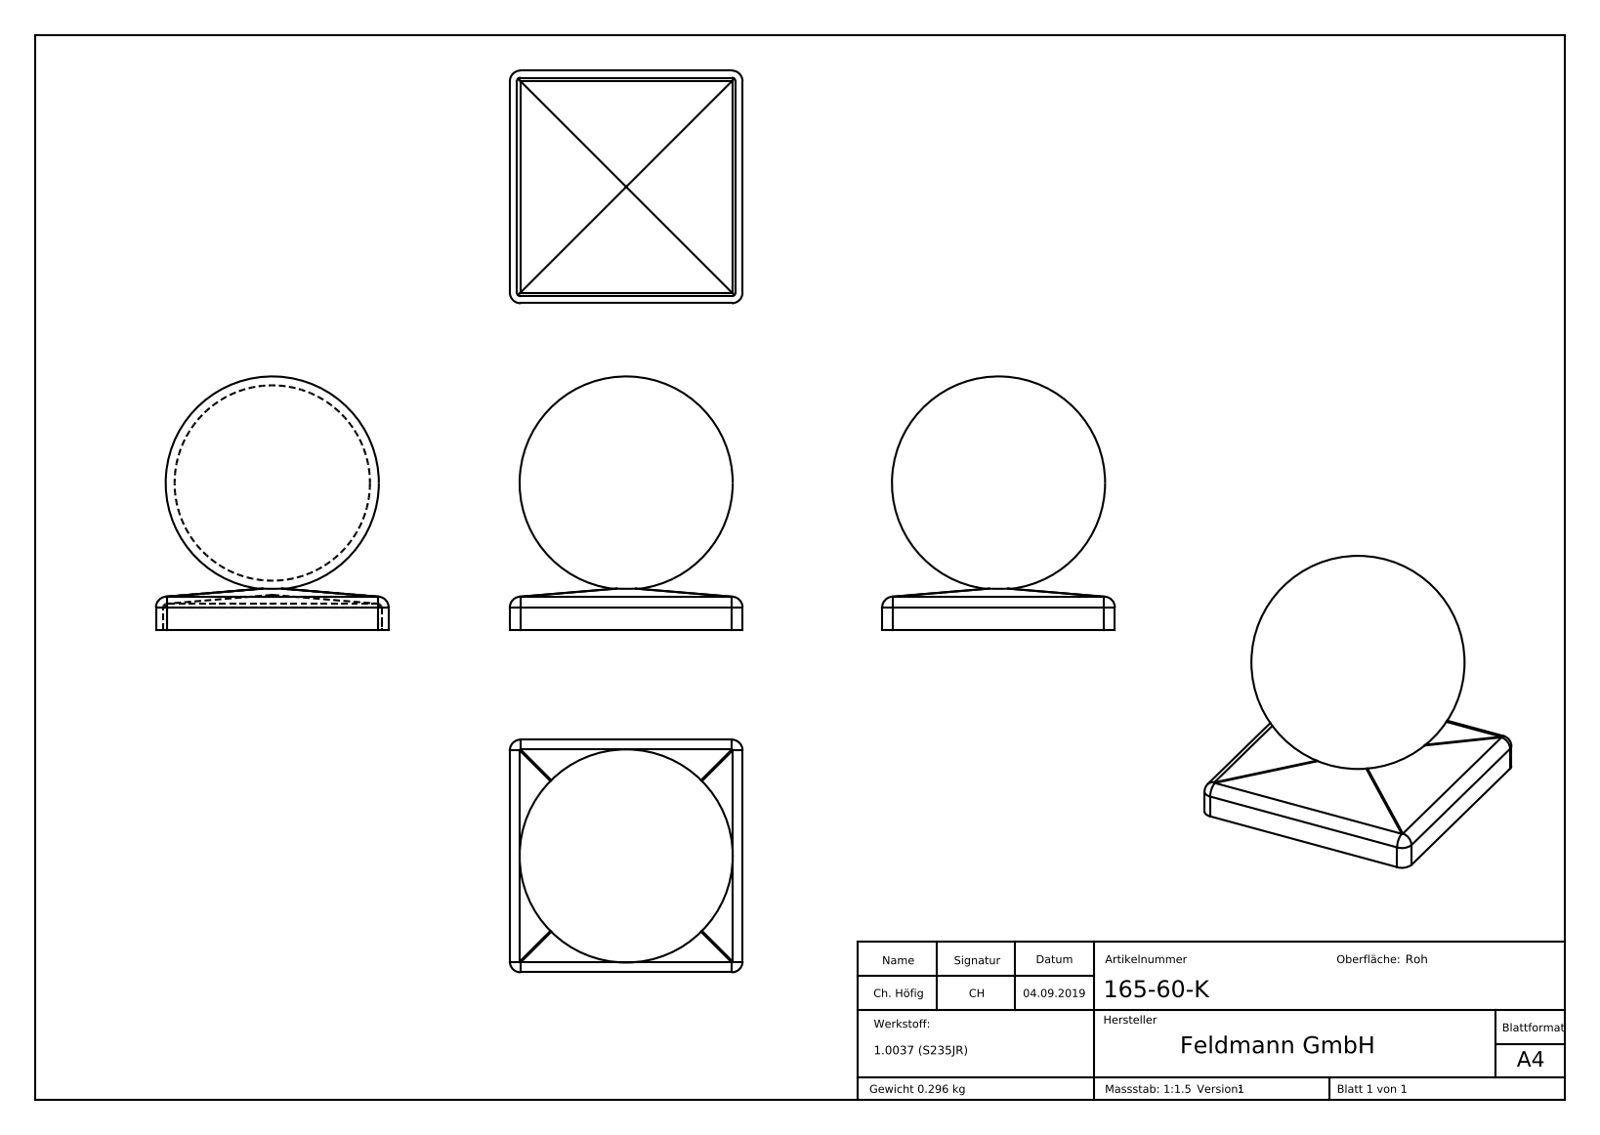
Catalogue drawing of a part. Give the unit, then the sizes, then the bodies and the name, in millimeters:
Units: millimetres
Overall size (bounding box): 71.5 × 65.5 × 65.5
Partial cylindrical surfaces — rounded edges, fillets, slot ends (radius × count): R3 ×12, R1 ×10
Main face-to-face distances: 2, 63.5, 65.5, 61.5, 1.9, 61.6, 63.6, 6.36, 1, 0.58
Volume: 37 886 mm³ · Surface area: 33 161 mm²
Bodies: 1 solid, 334 faces (170 planar, 24 cylindrical, 140 other)
Part name (STEP PRODUCT): 165-60-K
STEP written by: SolidWorks 2015 (CONFIG_CONTROL_DESIGN)
